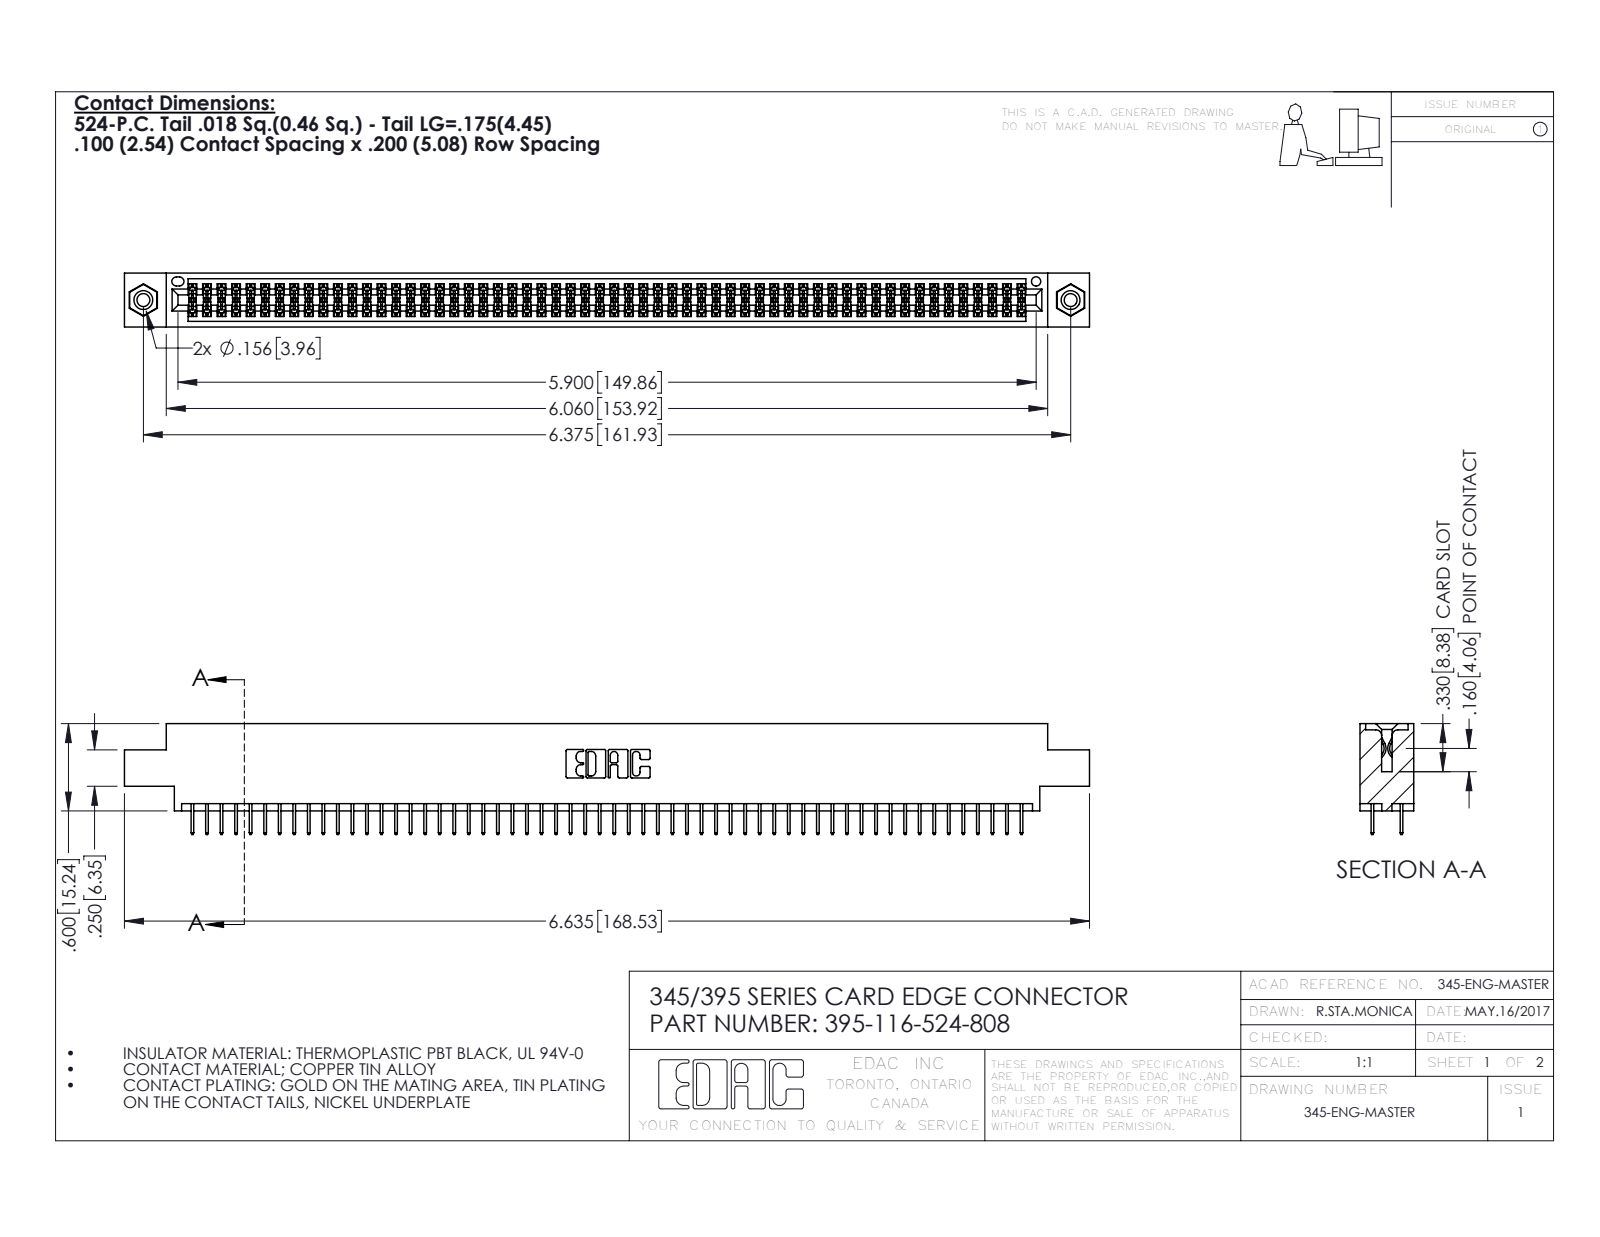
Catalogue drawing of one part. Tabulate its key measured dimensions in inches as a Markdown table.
| quantity | value |
| --- | --- |
| part name | 345-292-001_345-293-124; 395-116-524-808; 345-250-001_345-250-003-102; 345 Part_0.170 Offset - 0.156 Dia-TI |
| STEP written by | SolidWorks 2016 (CONFIG_CONTROL_DESIGN) |
| units | inches |
| bodies | 119 solids, 6454 faces (4640 planar, 1798 cylindrical, 16 other) |
| overall size | 6.635 × 0.762 × 0.37 |
| volume | 0.99 in³ |
| surface area | 37.18 in² |
| round holes (diameter × count) | 0.089 × 2, 0.125 × 2, 0.156 × 2, 0.064 × 1 |
| round bosses / shafts (diameter × count) | 0.155 × 2 |
| partial cylindrical surfaces (radius × count) | 0.006 × 174, 0.01 × 22, 0.007 × 6, 0.031 × 6, 0.026 × 3, 0.014 × 2, 0.019 × 2, 0.022 × 2 |
| main face-to-face distances | 0.072, 0.298, 0.37, 0.2, 0.098, 0.272, 0.025, 0.225, 0.072, 0.175 |
| hole center spacings | 0.27, 6.139, 6.375 |
